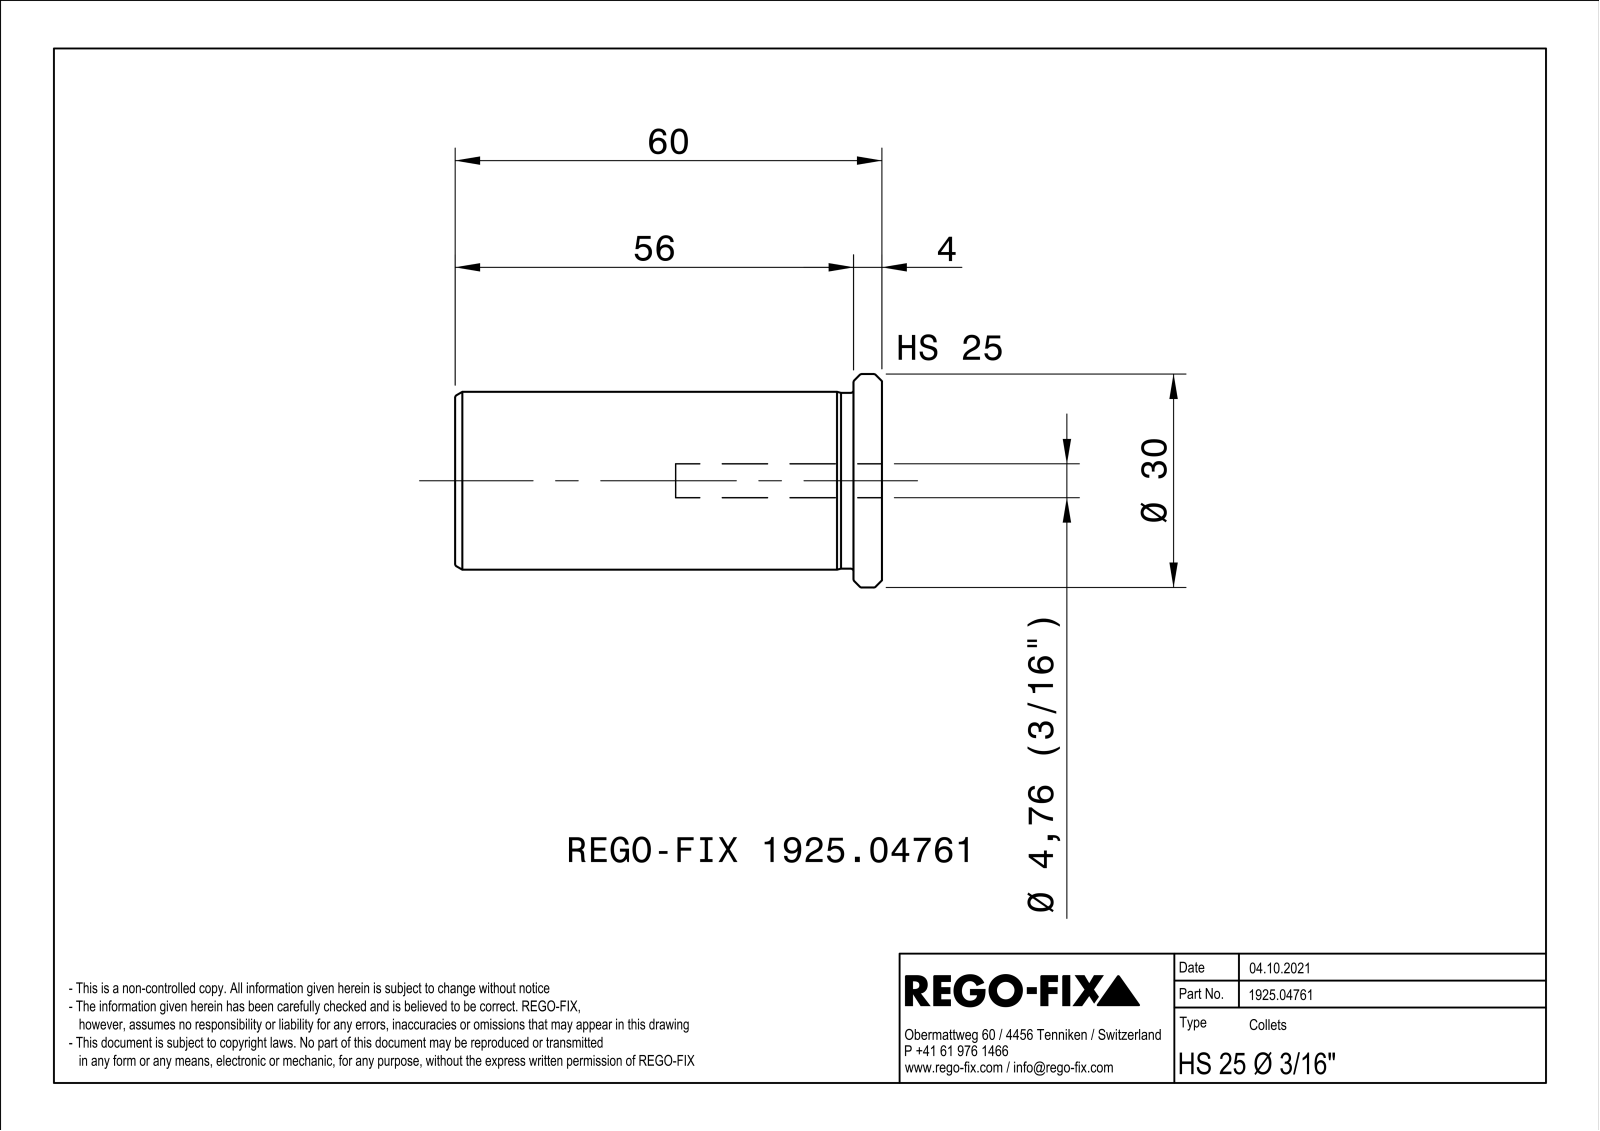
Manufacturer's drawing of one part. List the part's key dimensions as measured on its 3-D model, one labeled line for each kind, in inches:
Part name (STEP PRODUCT): NOCUT
STEP written by: SIEMENS PLM Software Solid Edge ST10 (AUTOMOTIVE_DESIGN)
Units: inches
Bodies: 1 solid, 73 faces (22 planar, 12 cylindrical, 39 other)
Overall size (bounding box): 2.362 × 1.181 × 1.181
Volume: 1.423 in³ · Surface area: 15.37 in²
Round holes (diameter × count): ⌀0.187 ×1, ⌀0.394 ×1, ⌀0.807 ×1
Round bosses / shafts (diameter × count): ⌀1.181 ×1, ⌀0.984 ×1, ⌀0.972 ×1
Main face-to-face distances: 0.031, 0.157, 2.362, 2.205
